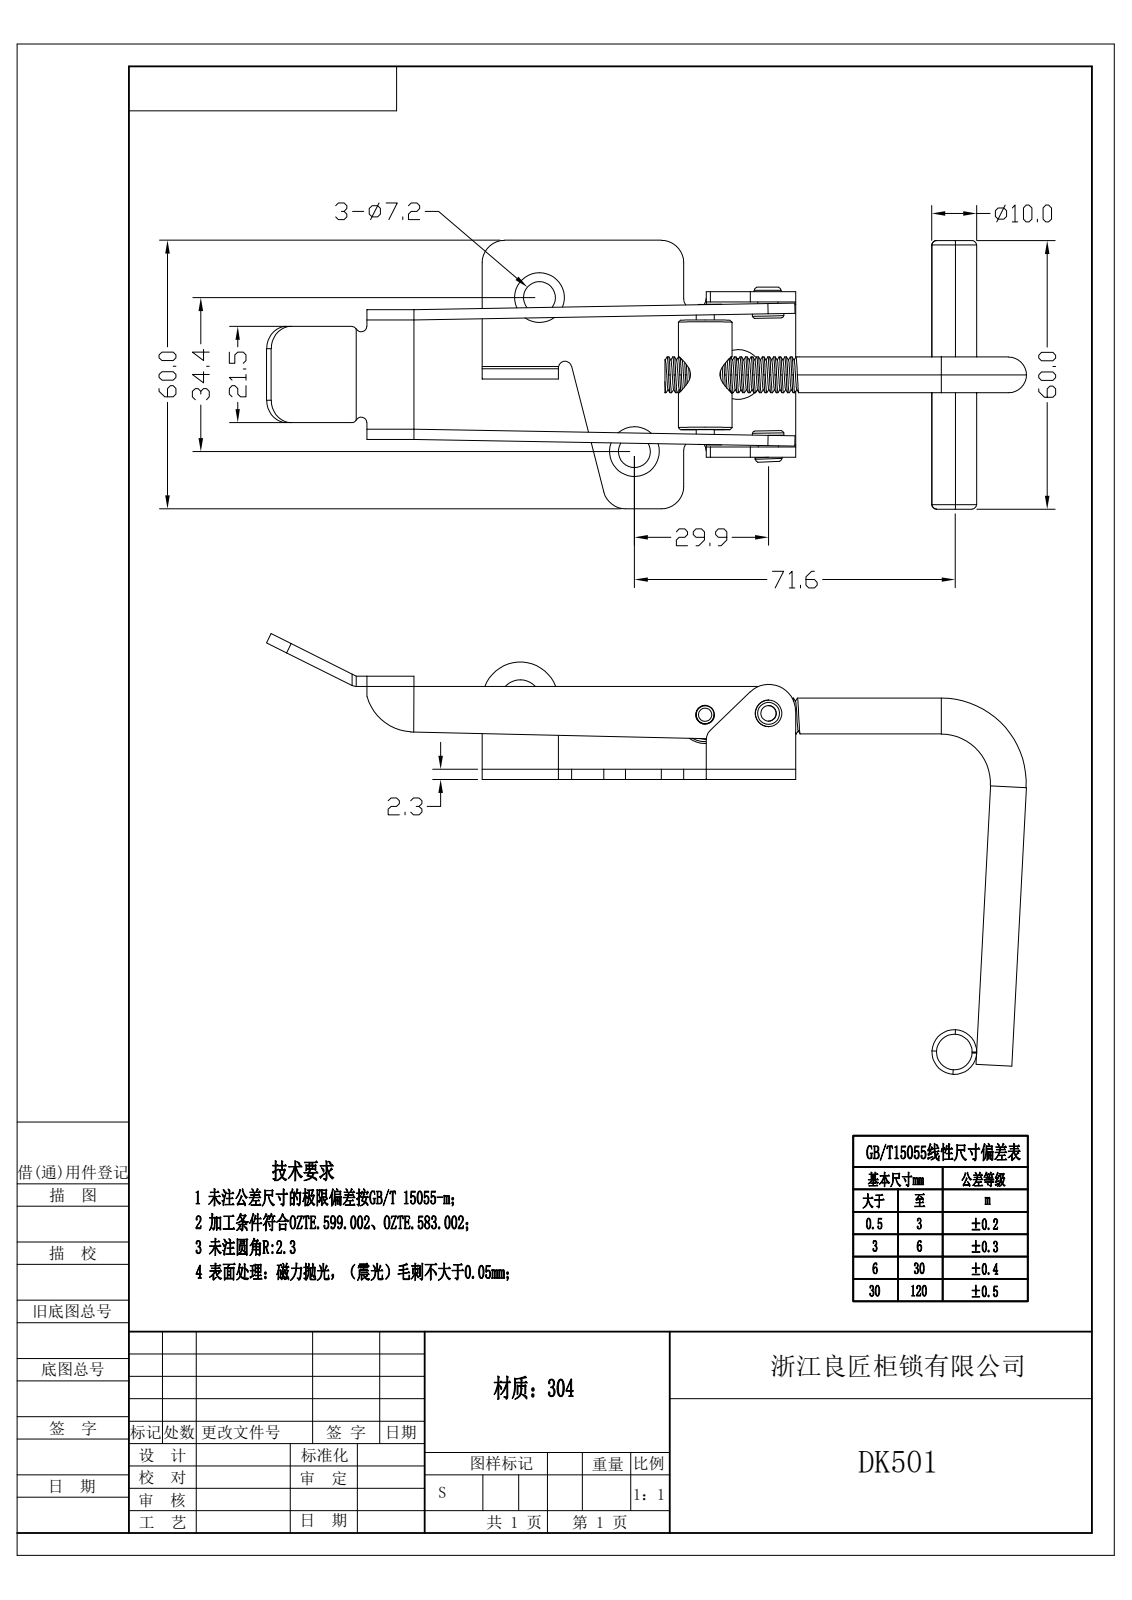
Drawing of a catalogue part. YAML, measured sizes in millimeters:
step_written_by: "Rhino 8.5 (CONFIG_CONTROL_DESIGN)"
units: millimeters
bodies: {solids: 7, faces: 257, planar: 87, cylindrical: 137, other: 33}
overall_size: [167.45, 97.94, 60.06]
volume: 20850
surface_area: 23453
round_holes:
  - {diameter: 2.8, count: 1}
  - {diameter: 3, count: 1}
  - {diameter: 3.62, count: 1}
  - {diameter: 4, count: 1}
  - {diameter: 9, count: 1}
round_bosses_or_shafts:
  - {diameter: 8, count: 2}
  - {diameter: 12, count: 1}
  - {diameter: 10, count: 1}
  - {diameter: 6.47, count: 1}
  - {diameter: 5.95, count: 1}
partial_cylinders:
  - {radius: 0.5, count: 6}
  - {radius: 5, count: 6}
  - {radius: 2.3, count: 5}
  - {radius: 1.19, count: 2}
  - {radius: 10.79, count: 2}
  - {radius: 1.5, count: 1}
  - {radius: 2.43, count: 1}
  - {radius: 3, count: 1}
face_to_face_distances: [2.3, 20.8, 18.5, 17.91, 16.73, 34.64, 2.29, 23.1, 20.21, 36.94]
hole_center_spacings: [14.59, 41.39, 55.93]
